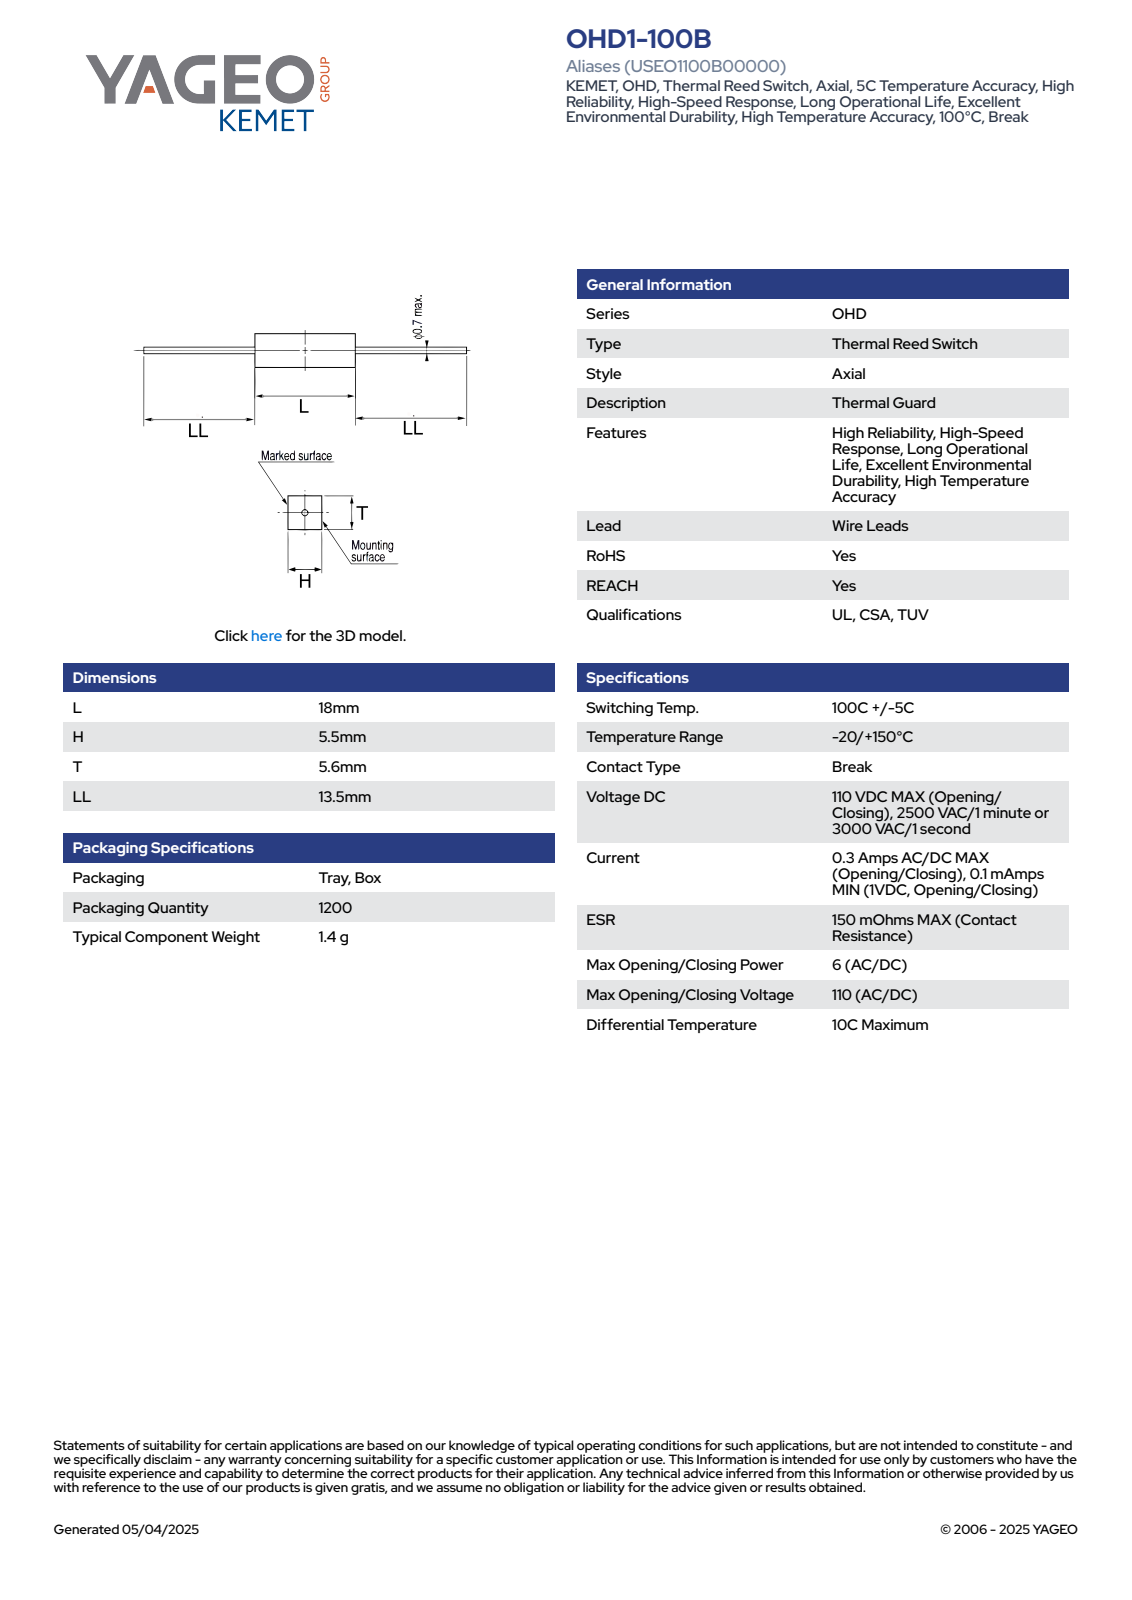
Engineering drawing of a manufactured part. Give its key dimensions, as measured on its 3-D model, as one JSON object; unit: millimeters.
{"part_name": "ST_OHD1_L18H5.5T5.6LL13.5", "step_written_by": "SolidWorks 2014 (AUTOMOTIVE_DESIGN)", "units": "millimeters", "bodies": {"solids": 1, "faces": 66, "planar": 62, "cylindrical": 4, "other": 0}, "overall_size": [45, 5.6, 5.5], "volume_mm3": 565, "surface_area_mm2": 521, "round_bosses_or_shafts": [[0.7, 1]], "face_to_face_distances": [5.5, 5.6, 18, 13.5, 31.5, 45, 3.76, 1.84, 1.74, 2.02]}
